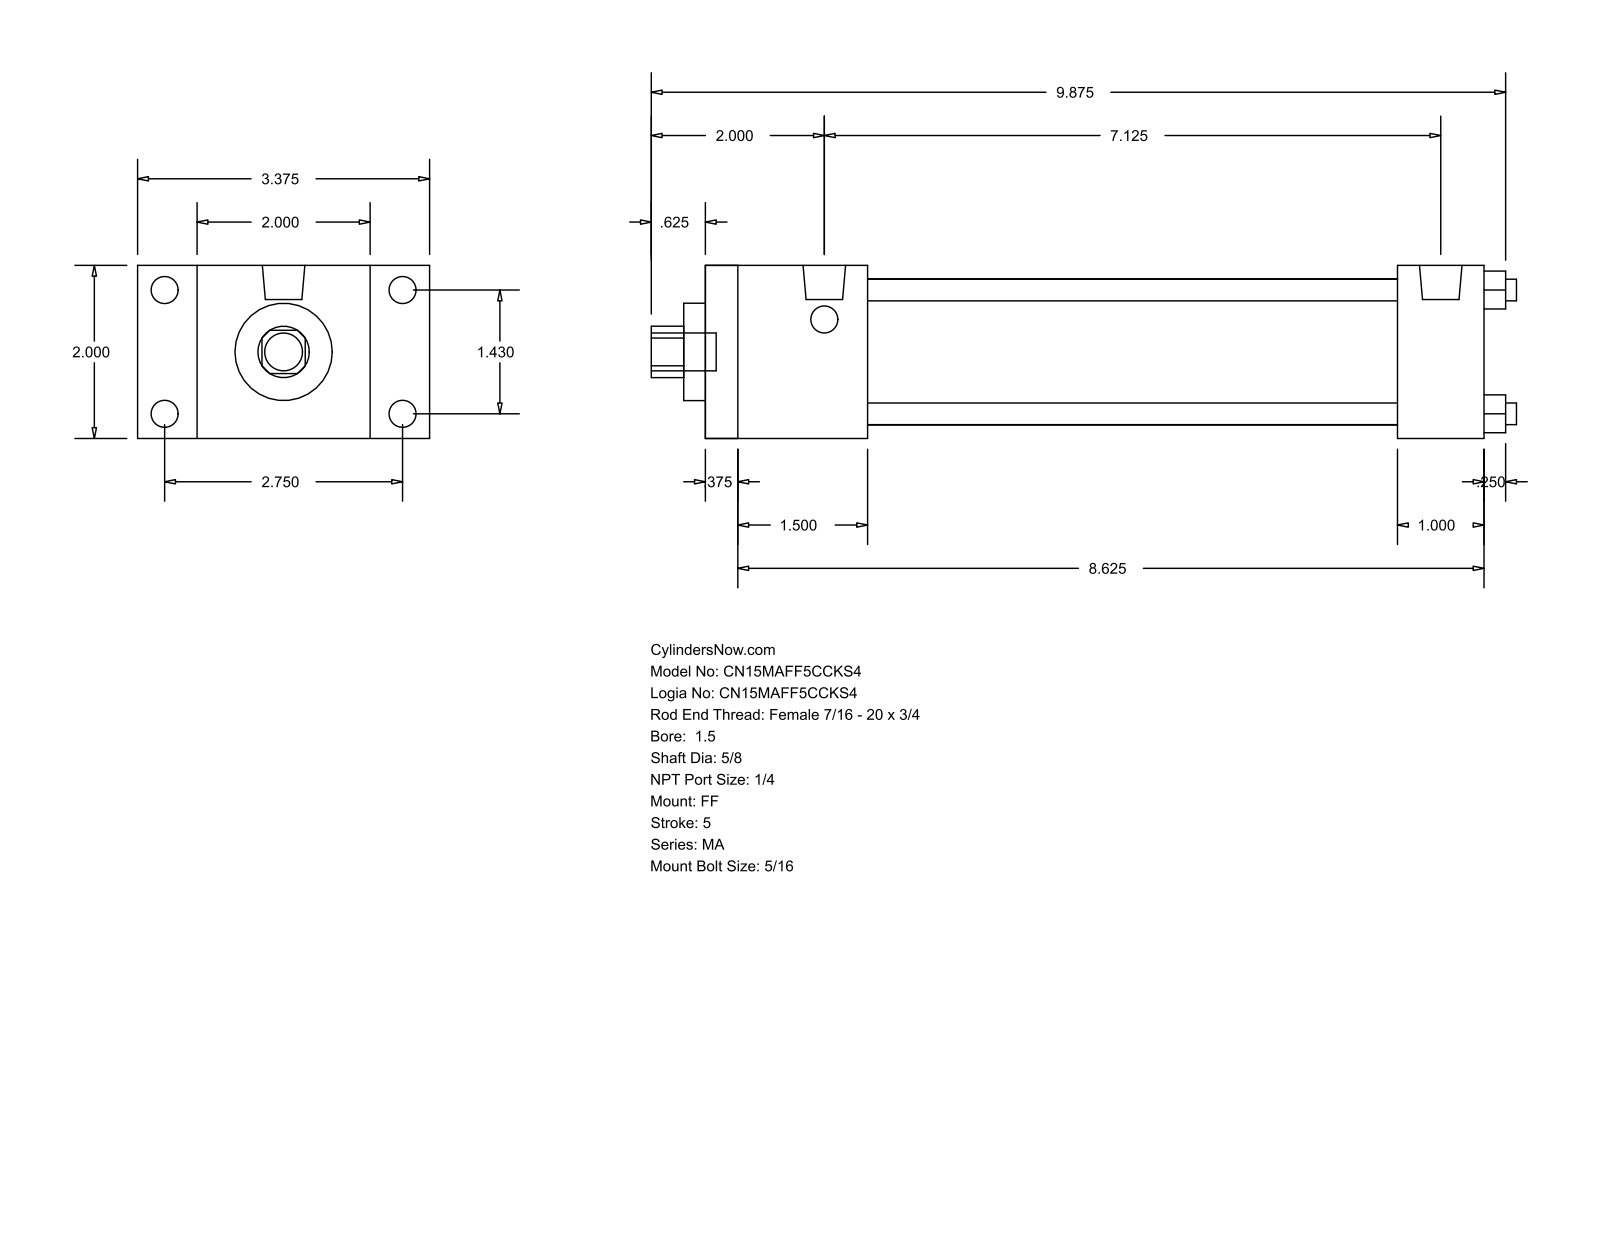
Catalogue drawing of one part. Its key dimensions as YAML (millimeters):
part_name: "MA_FF__0150_0.625"
step_written_by: "GSSL Pune (CONFIG_CONTROL_DESIGN)"
units: millimeters
bodies: {solids: 0, faces: 92, planar: 64, cylindrical: 28, other: 0}
overall_size: [254, 85.72, 50.8]
round_holes:
  - {diameter: 6.35, count: 4}
  - {diameter: 15.88, count: 1}
  - {diameter: 28.57, count: 1}
  - {diameter: 42.93, count: 1}
round_bosses_or_shafts:
  - {diameter: 7.94, count: 8}
  - {diameter: 12.49, count: 2}
  - {diameter: 11.11, count: 1}
partial_cylinders:
  - {radius: 7.54, count: 1}
face_to_face_distances: [50.8, 228.59, 9.52, 219.07, 25.4, 47.62, 203.19, 38.1, 193.67, 155.57]
hole_center_spacings: [25.68, 36.32, 51.36]
